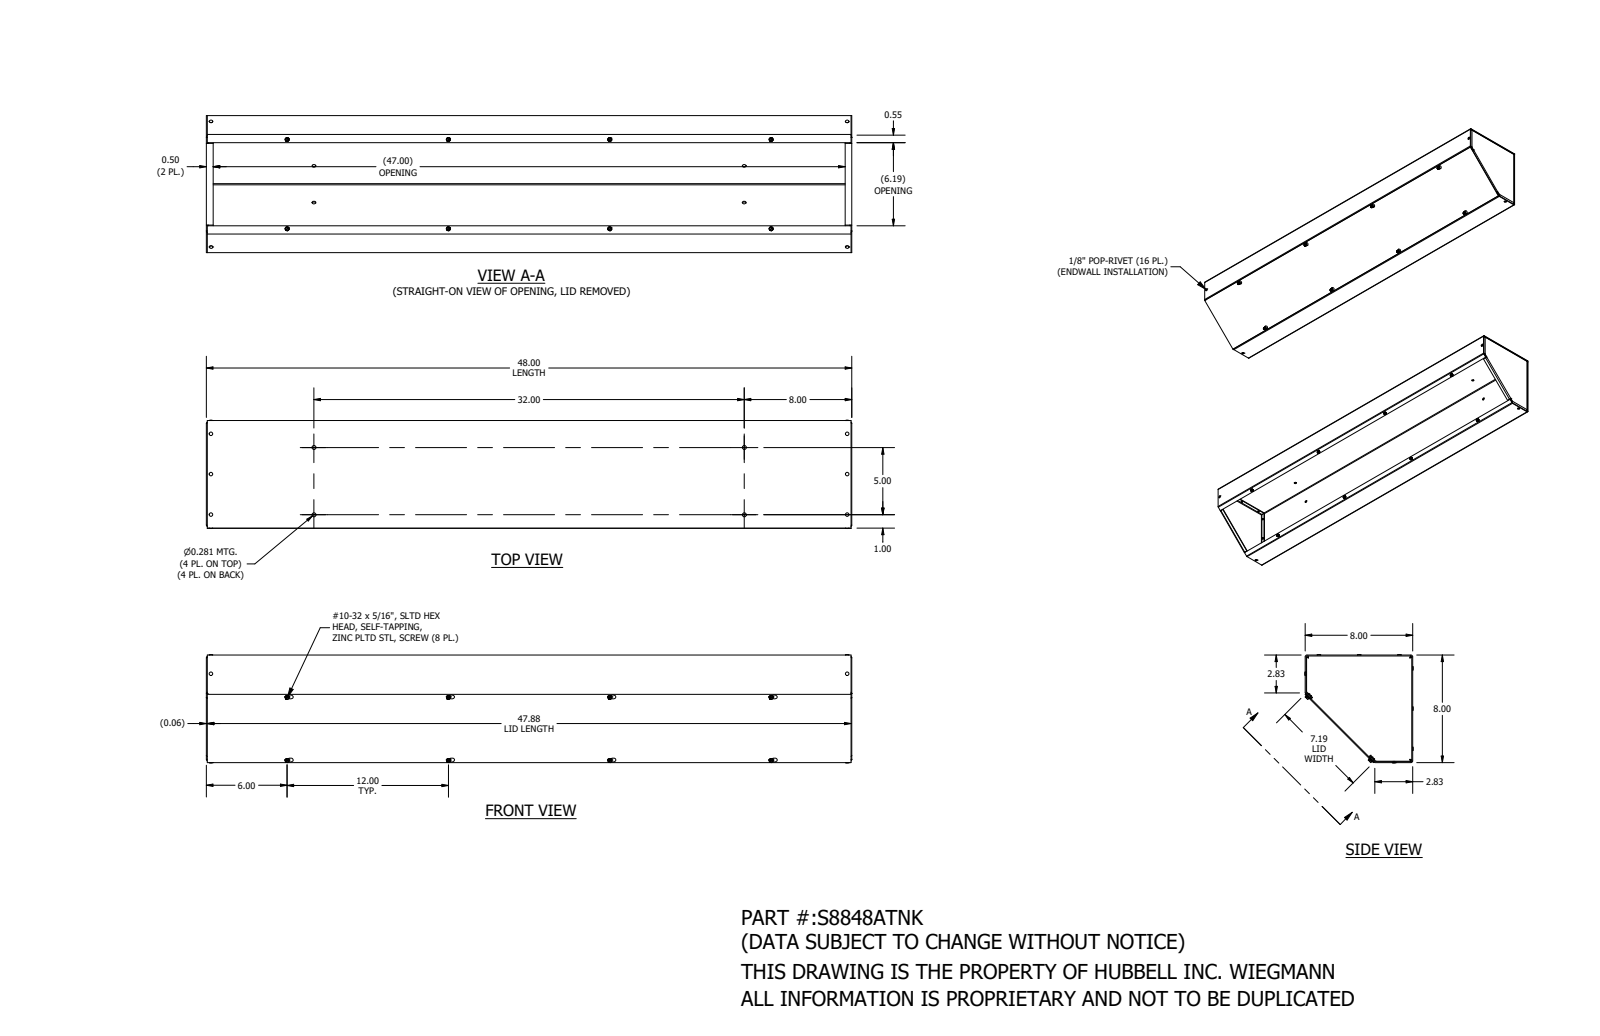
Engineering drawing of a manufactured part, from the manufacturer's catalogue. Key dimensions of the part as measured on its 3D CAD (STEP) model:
Part name (STEP PRODUCT): S8848ATNK
STEP written by: SolidWorks 2021 (AUTOMOTIVE_DESIGN)
Units: inches
Bodies: 28 solids, 1648 faces (376 planar, 440 cylindrical, 832 other)
Overall size (bounding box): 48 × 8.08 × 8.08
Volume: 113.4 in³ · Surface area: 3 095 in²
Round holes (diameter × count): ⌀0.129 ×16, ⌀0.171 ×8, ⌀0.281 ×8, ⌀0.406 ×8
Round bosses / shafts (diameter × count): ⌀0.262 ×16, ⌀0.125 ×9, ⌀0.313 ×8, ⌀0.181 ×8, ⌀0.125 ×7
Partial cylindrical surfaces — rounded edges, fillets, slot ends (radius × count): R0.064 ×32, R0.136 ×15, R0.062 ×9, R0.109 ×8, R0.063 ×6
Main face-to-face distances: 0.074, 7.926, 7.852, 8, 0.068, 47.926, 0.142, 47.852, 48, 0.148
Hole centre spacings: 12, 0.25, 3, 24, 47.313, 47.407, 11.75, 12.25
